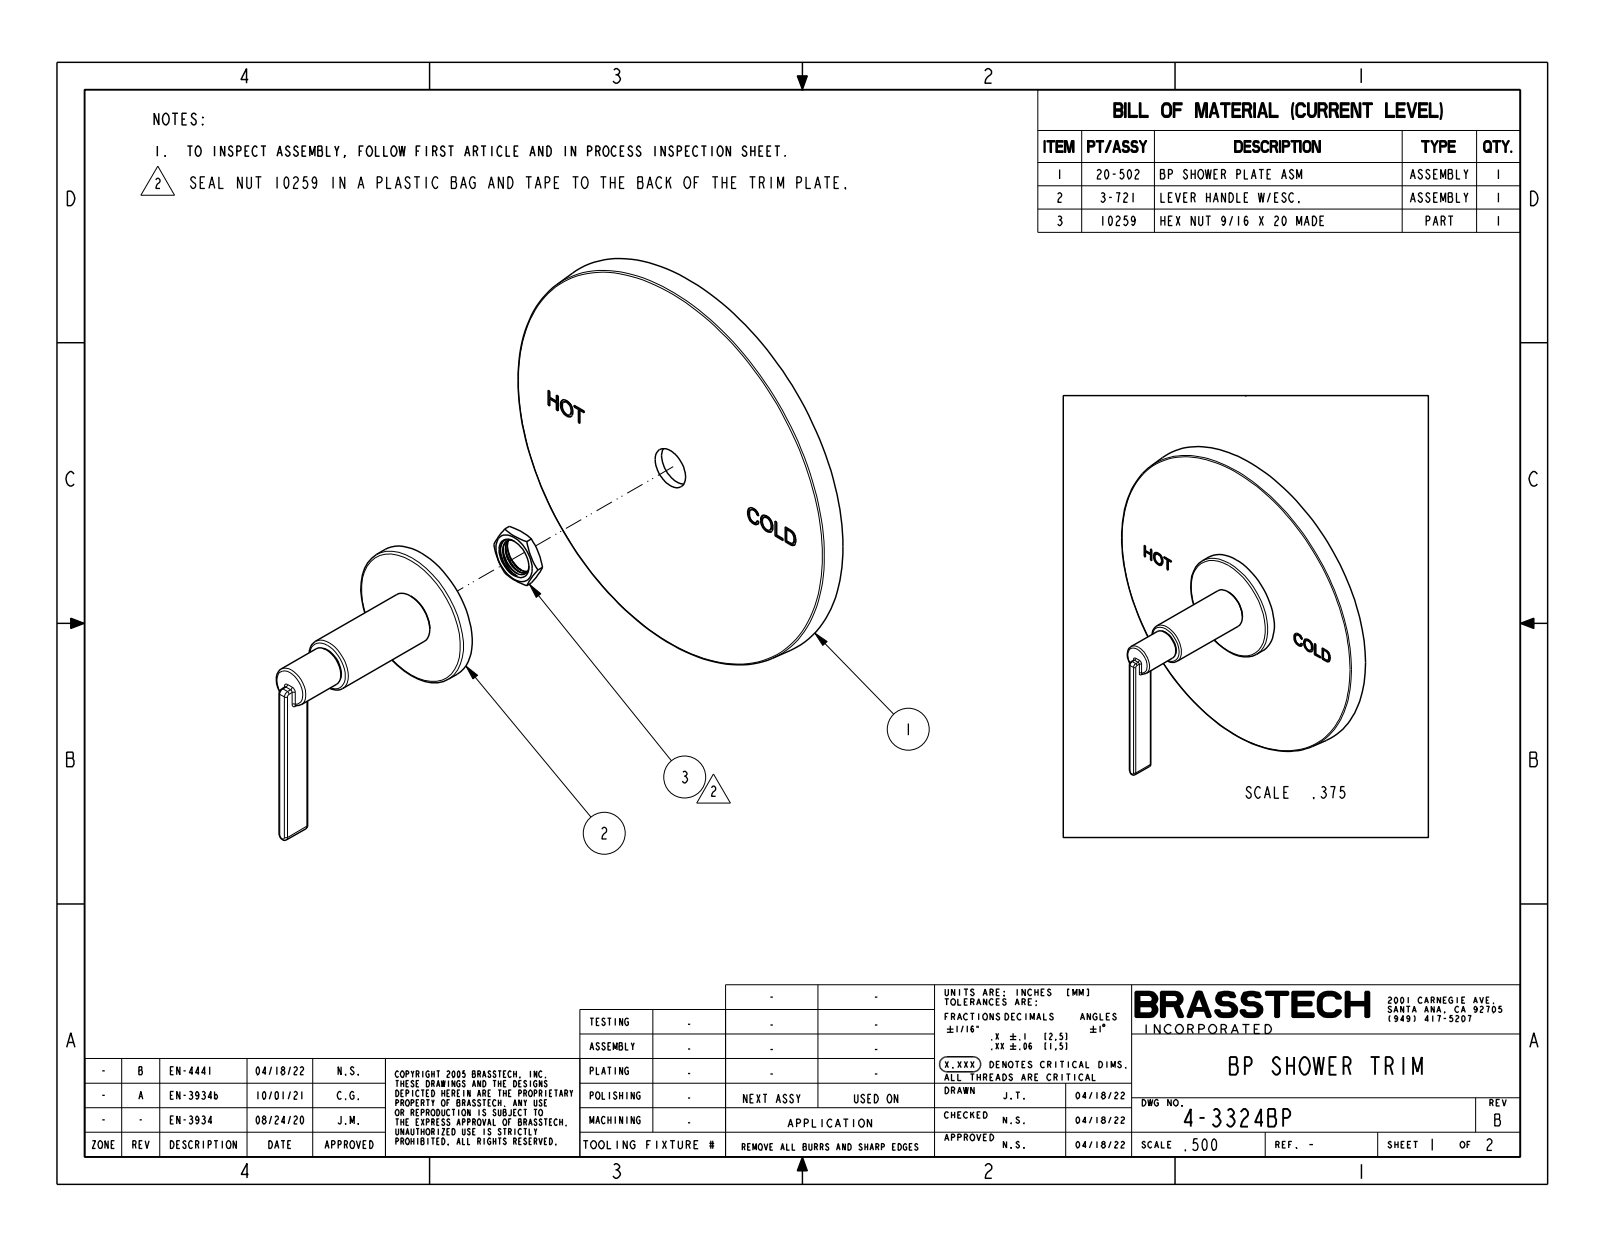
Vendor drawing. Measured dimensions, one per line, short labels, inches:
name: 30749; 20-502_ASM; 13532; 20-565_ASM (+5 more)
written by: CREO PARAMETRIC BY PTC INC, 2018400 (CONFIG_CONTROL_DESIGN)
unit: in
bodies: 4 solids, 335 faces (113 planar, 95 cylindrical, 127 other)
size: 6 × 5.994 × 2.981
volume: 4.865 in³; area: 86.84 in²
holes: 1× ⌀0.11, 1× ⌀0.36, 1× ⌀0.397, 1× ⌀0.4, 1× ⌀0.516, 1× ⌀0.535, 1× ⌀0.59, 1× ⌀0.6, 1× ⌀0.7, 1× ⌀1.6, 1× ⌀1.89
bosses: 1× ⌀2, 1× ⌀1.65, 1× ⌀0.75, 1× ⌀0.73, 1× ⌀0.68, 1× ⌀0.563, 1× ⌀0.51
rounds: 11× R0.03, 1× R0.06, 1× R0.075, 1× R0.137
face distances: 0.125, 0.325, 0.2, 0.225, 0.35, 0.55, 0.15, 0.05, 0.5, 0.275
